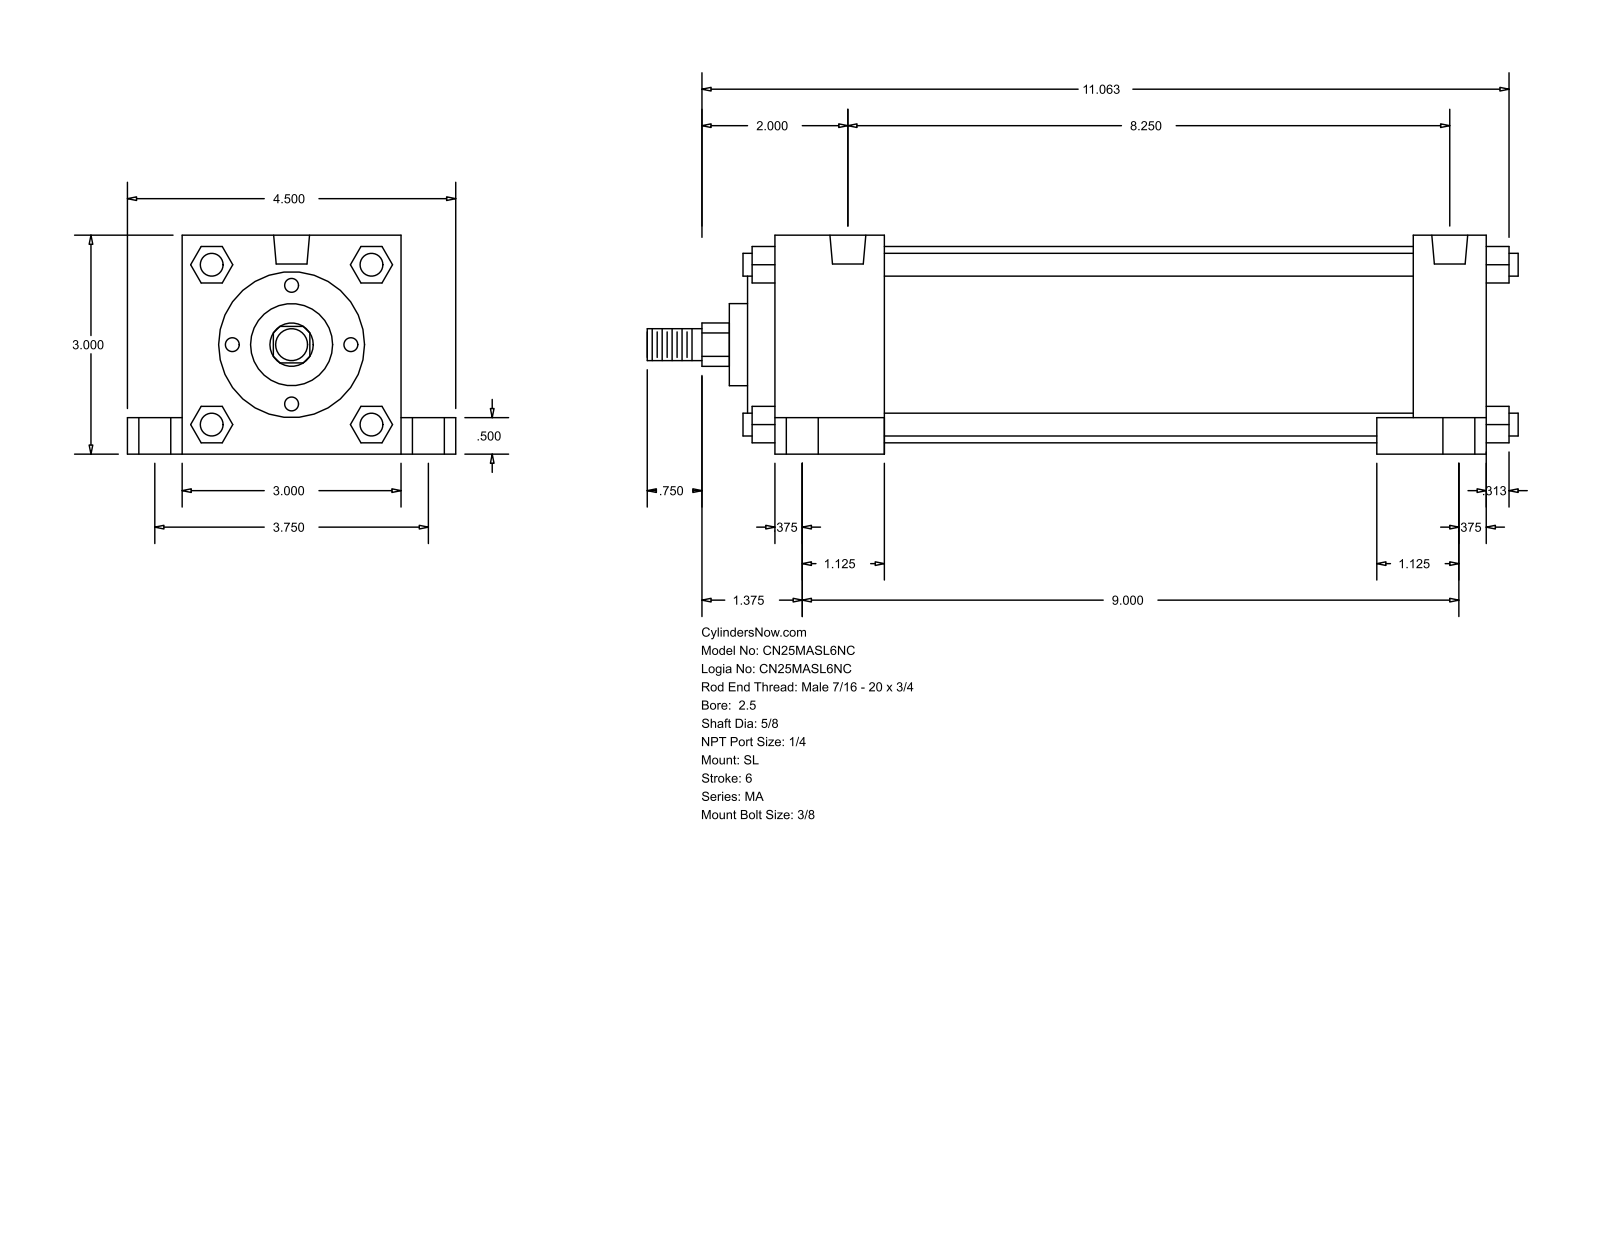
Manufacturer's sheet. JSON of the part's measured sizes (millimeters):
{"part_name": "MA_SL__0250_0.625", "step_written_by": "GSSL Pune (CONFIG_CONTROL_DESIGN)", "units": "millimeters", "bodies": {"solids": 0, "faces": 150, "planar": 113, "cylindrical": 37, "other": 0}, "overall_size": [303.21, 114.3, 76.2], "round_holes": [[7.94, 4], [11.11, 4], [17.46, 4], [12.49, 2]], "round_bosses_or_shafts": [[7.94, 4], [68.33, 1], [50.8, 1], [28.57, 1], [15.88, 1], [11.11, 1]], "partial_cylinders_radius": [[7.54, 1]], "face_to_face_distances": [76.2, 247.65, 12.7, 184.15, 25.4, 38.1, 209.55, 222.25, 19.05, 63.5], "hole_center_spacings": [47.73, 50.2, 95.24, 209.55, 217.99, 228.6, 230.4, 247.65]}
